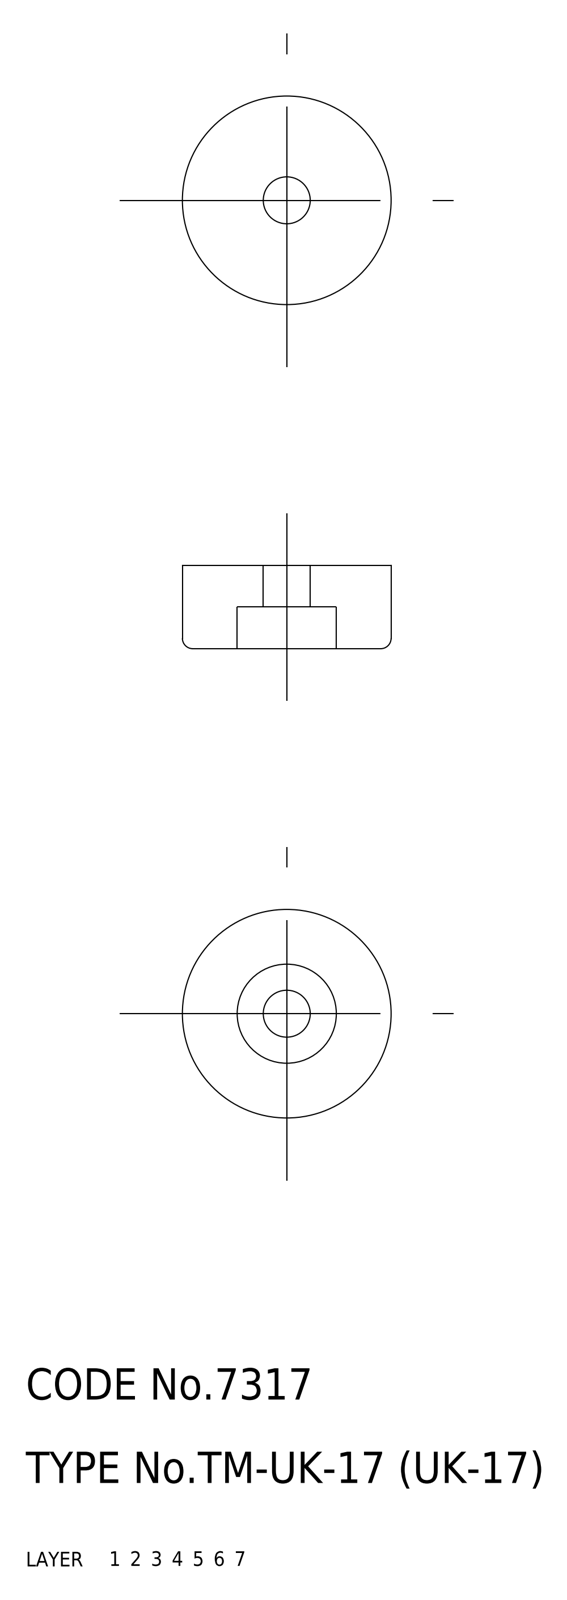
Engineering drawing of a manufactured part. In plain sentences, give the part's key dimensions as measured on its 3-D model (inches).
The part is named "washer; rubber foot; UK_17_10837_36". Its 3-D file was written by "CADfix (AUTOMOTIVE_DESIGN)". It is 2 solids with 23 faces: 0 planar, 0 cylindrical and 23 other. Overall it measures 0.787 by 0.787 by 0.315 inches. Its volume is 0.132 cubic inches and its surface area 2.44 square inches.
